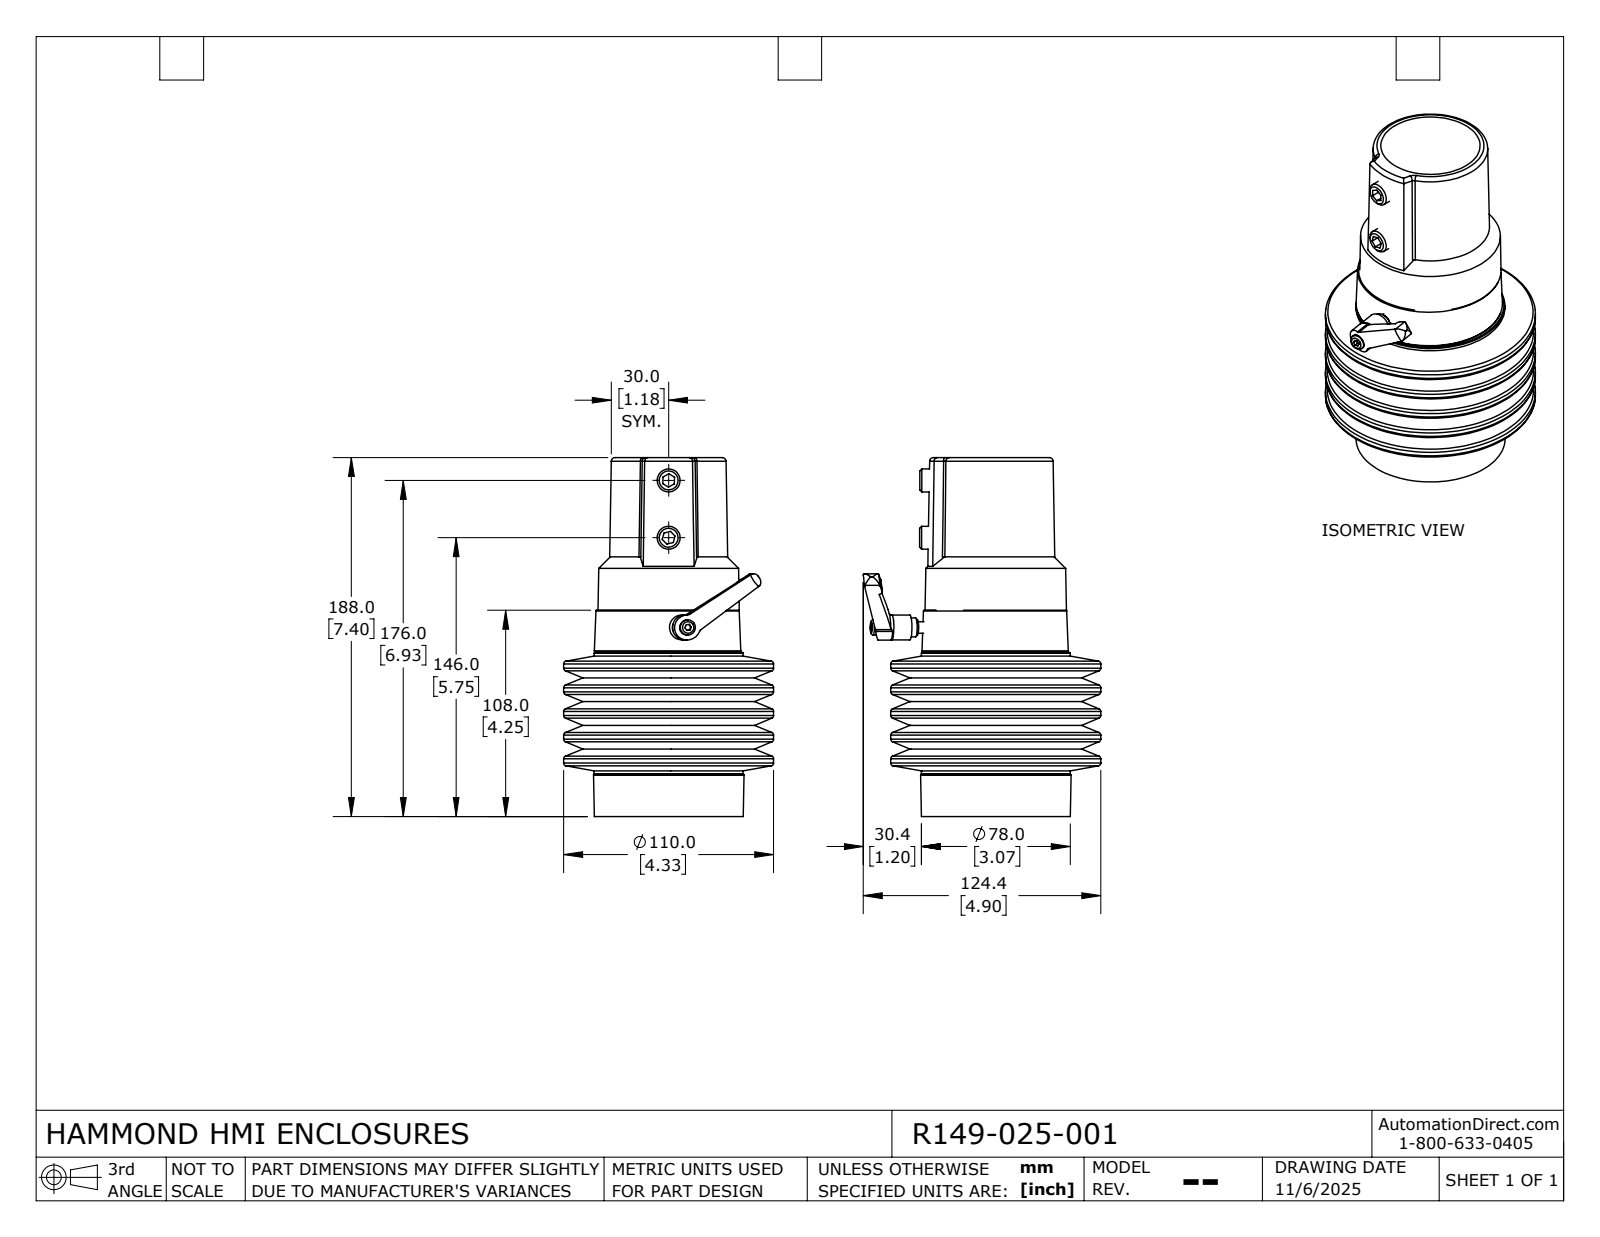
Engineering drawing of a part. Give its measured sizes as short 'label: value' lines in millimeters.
name: R149-025-001
written by: SolidWorks 2024 (AUTOMOTIVE_DESIGN)
unit: mm
bodies: 10 solids, 405 faces (97 planar, 148 cylindrical, 160 other)
size: 384 × 124.42 × 110
volume: 454 119 mm³; area: 255 213 mm²
holes: 4× ⌀4.92, 2× ⌀6, 2× ⌀10.11, 2× ⌀72, 1× ⌀4.92, 1× ⌀40, 1× ⌀45, 1× ⌀48.38, 1× ⌀51, 1× ⌀52.6, 1× ⌀86, 1× ⌀106
bosses: 2× ⌀86, 2× ⌀12, 2× ⌀6, 1× ⌀110, 1× ⌀78, 1× ⌀70.25, 1× ⌀51, 1× ⌀48
rounds: 56× R0.3, 24× R2, 4× R0.5, 4× R4.5, 1× R4, 1× R6.6, 1× R29.2, 1× R33.8
face distances: 46.13, 31, 77.13, 1, 76.13, 30, 107.13, 77, 107, 30.87
hole spacings: 45.96, 32.43, 32.49, 32.57, 65, 0.66, 0.75, 30
